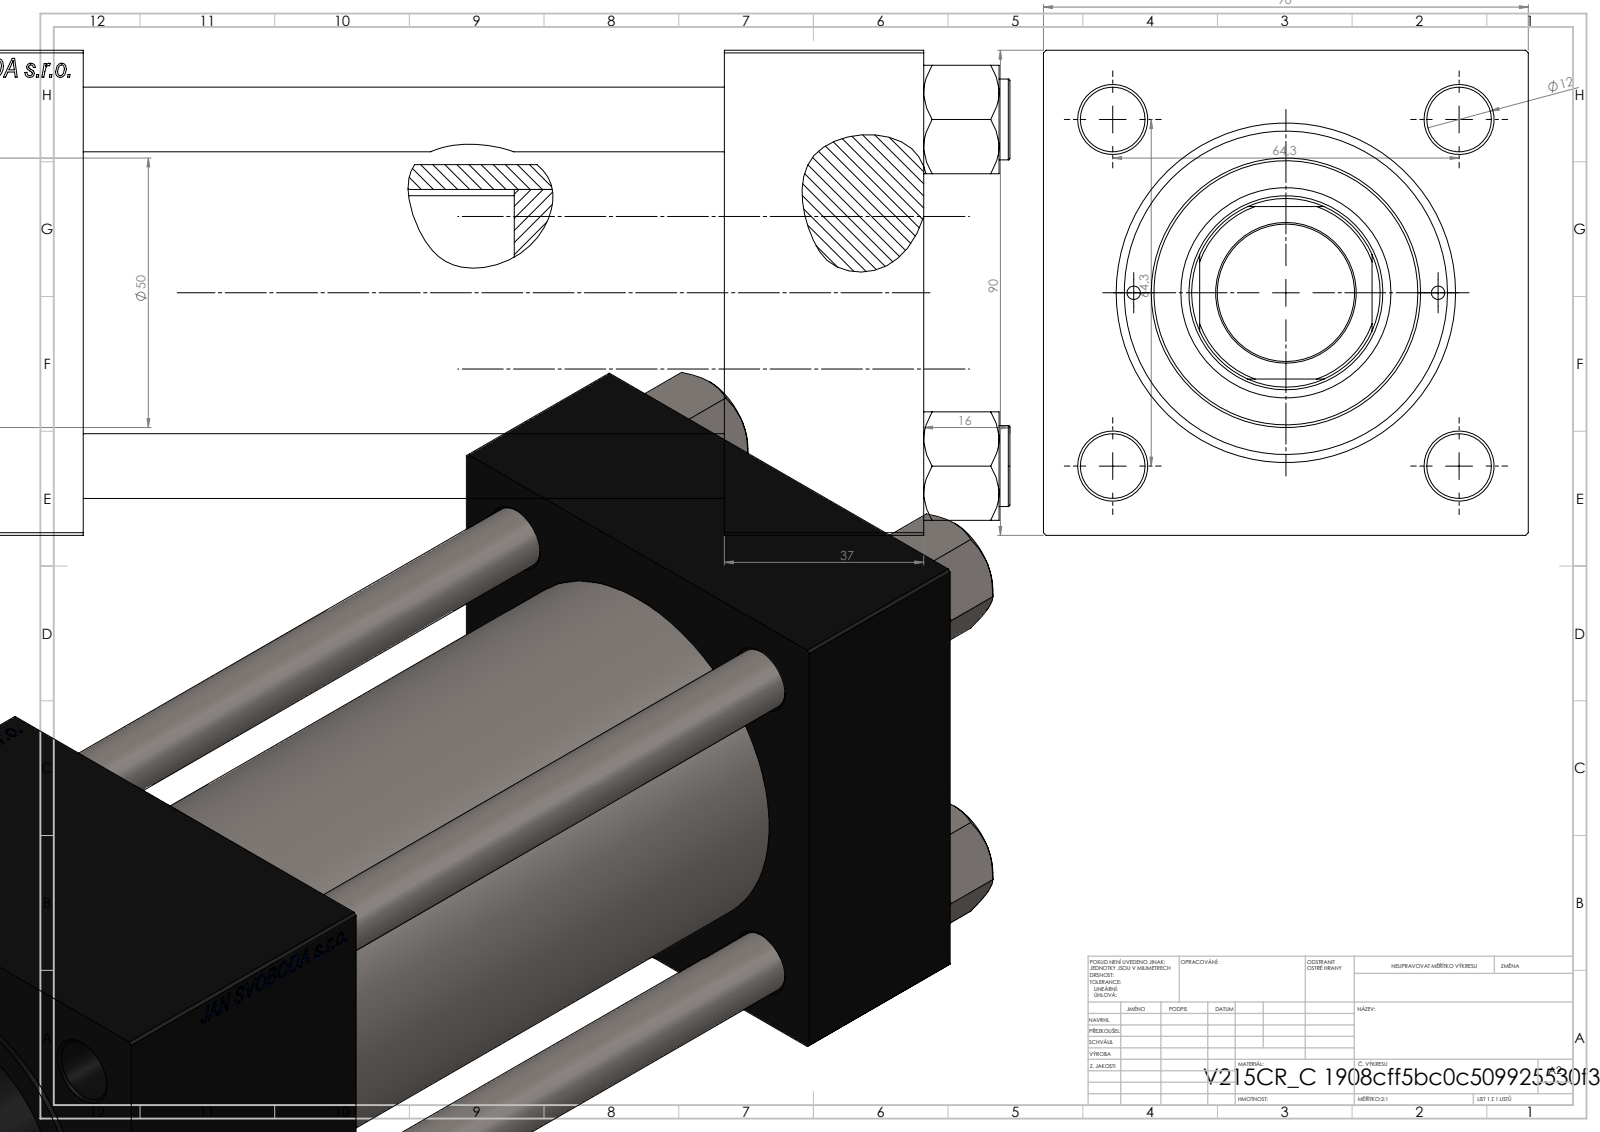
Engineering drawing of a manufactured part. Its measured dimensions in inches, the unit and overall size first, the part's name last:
Units: inches
Overall size (bounding box): 10.354 × 3.543 × 3.543
Round holes (diameter × count): ⌀0.472 ×4, ⌀0.098 ×2, ⌀0.276 ×2, ⌀0.825 ×2, ⌀1.181 ×2, ⌀1.004 ×1, ⌀1.417 ×1, ⌀1.535 ×1, ⌀1.969 ×1, ⌀2.362 ×1, ⌀2.48 ×1
Round bosses / shafts (diameter × count): ⌀0.591 ×4, ⌀2.717 ×1
Partial cylindrical surfaces — rounded edges, fillets, slot ends (radius × count): R0.689 ×1
Main face-to-face distances: 3.543, 1.457, 8.465, 7.008, 2.323, 6.142, 4.685, 7.335, 5.878, 1.193
Hole centre spacings: 1.275, 1.79, 2.531, 2.694, 1.112, 3.58, 2.224, 6.201
Volume: 66.7 in³ · Surface area: 348.8 in²
Bodies: 11 solids, 1154 faces (528 planar, 90 cylindrical, 536 other)
Part name (STEP PRODUCT): V215_VC_A; V215CR_C_TYCINKA; V215CR_C_Body; V215CR_VCP_C (+1 more)
STEP written by: SolidWorks 2019 (CONFIG_CONTROL_DESIGN)
